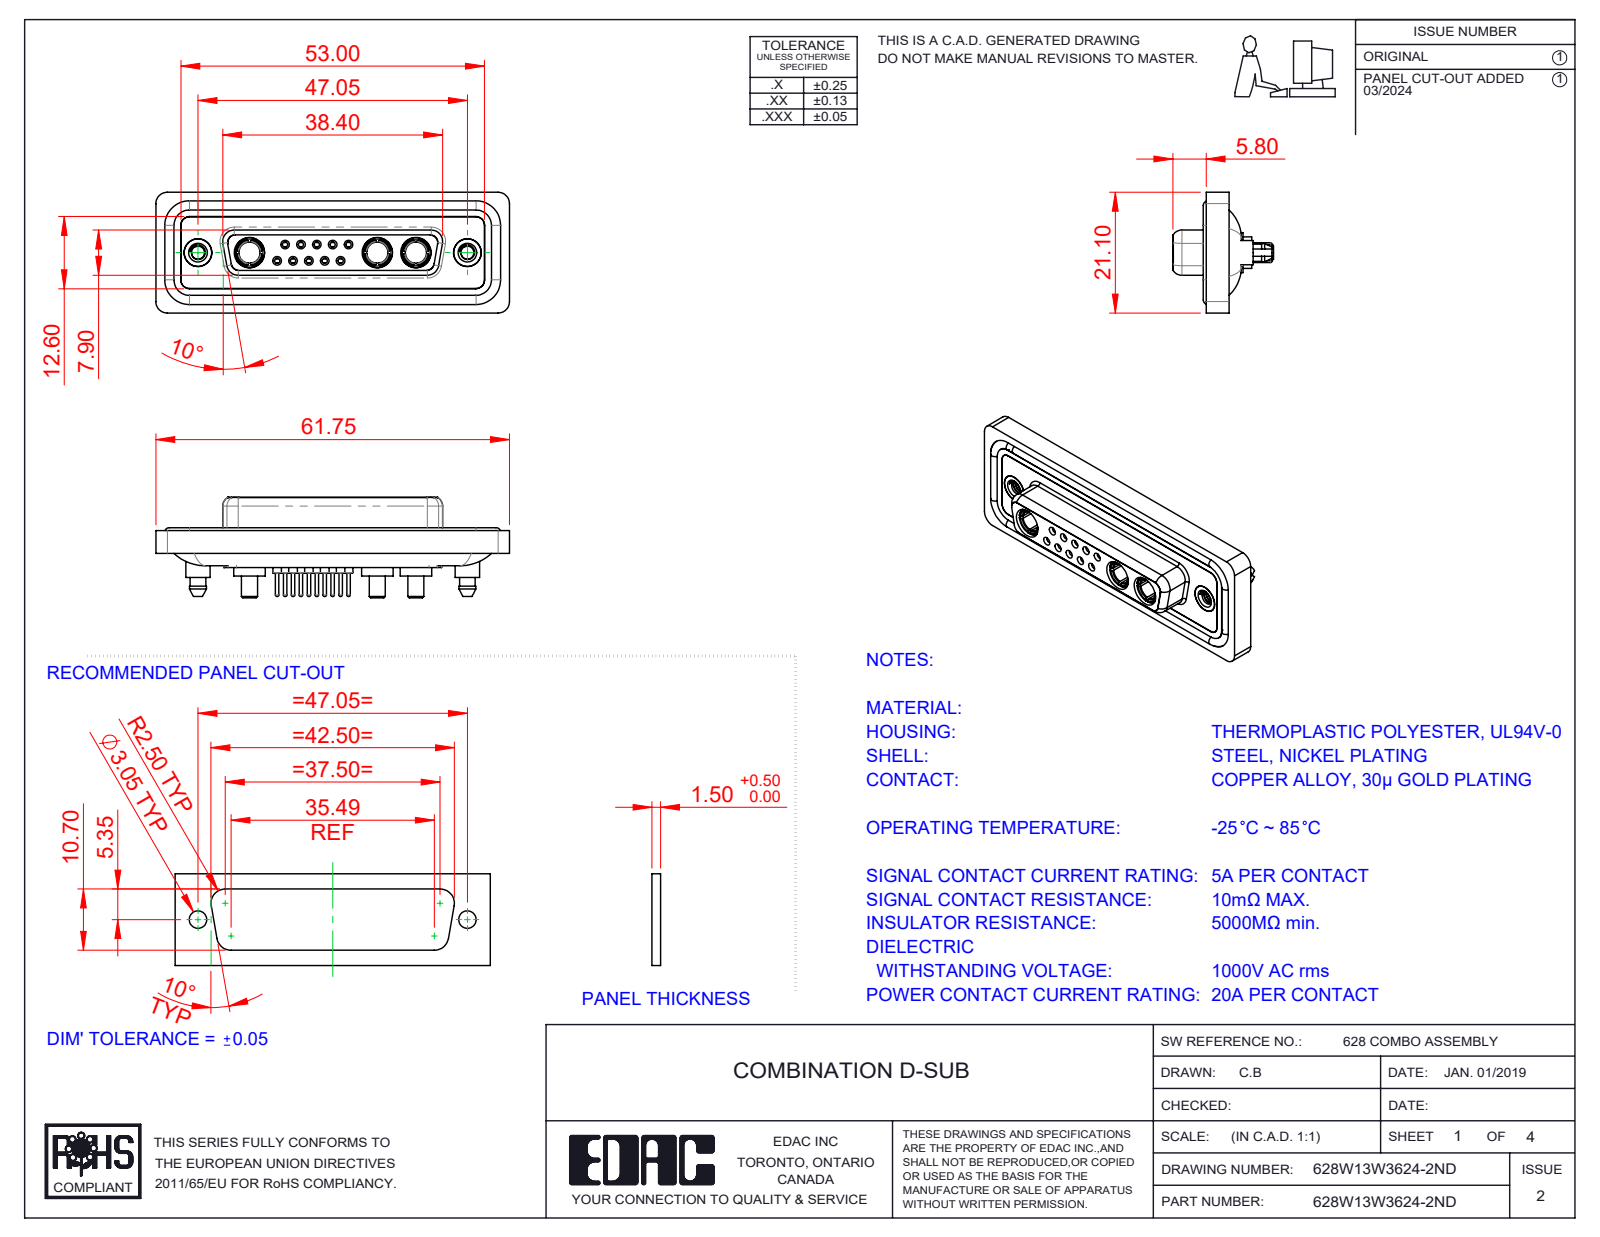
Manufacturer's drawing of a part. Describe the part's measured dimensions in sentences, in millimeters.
The part is named "628Combo Waterproof Housing_25 Contacts; 628W13W3624-2ND; 628Combo Housing_13W3; 628Combo Shell Front_25 Contacts (+5 more)". Its 3-D file was written by "SolidWorks 2023 (CONFIG_CONTROL_DESIGN)". It is 23 solids with 1224 faces: 358 planar, 495 cylindrical and 371 other. Overall it measures 61.75 by 21.1 by 17.55 millimeters. Its volume is 8 409 cubic millimeters and its surface area 14 048 square millimeters. Round holes: 10 of diameter 0.9, 10 of diameter 1.1, 10 of diameter 1.5, 10 of diameter 2, 5 of diameter 1.6, 5 of diameter 1.7, 5 of diameter 4.85, 3 of diameter 3.7, 3 of diameter 5.3, 2 of diameter 2.26, 2 of diameter 4, 2 of diameter 4.05. Round bosses or shafts: 10 of diameter 2.2, 10 of diameter 0.6, 9 of diameter 1.6, 3 of diameter 5.5, 3 of diameter 5.2, 3 of diameter 4.96, 3 of diameter 4.75, 3 of diameter 3.75. Partial cylindrical surfaces (rounded edges, fillets, slot ends): 24 of radius 1.5, 18 of radius 2, 10 of radius 1.6, 8 of radius 1.35, 4 of radius 0.25, 4 of radius 0.5, 4 of radius 0.6, 4 of radius 0.65. The main face-to-face distances are 0.4, 1.8, 7.45, 5.65, 0.5, 6.6, 7.05, 1.6, 2.9, 1.1. The hole center spacings are 3.16, 2.77, 5.03, 5.04, 5.54, 8.31, 7.49, 2.76.
